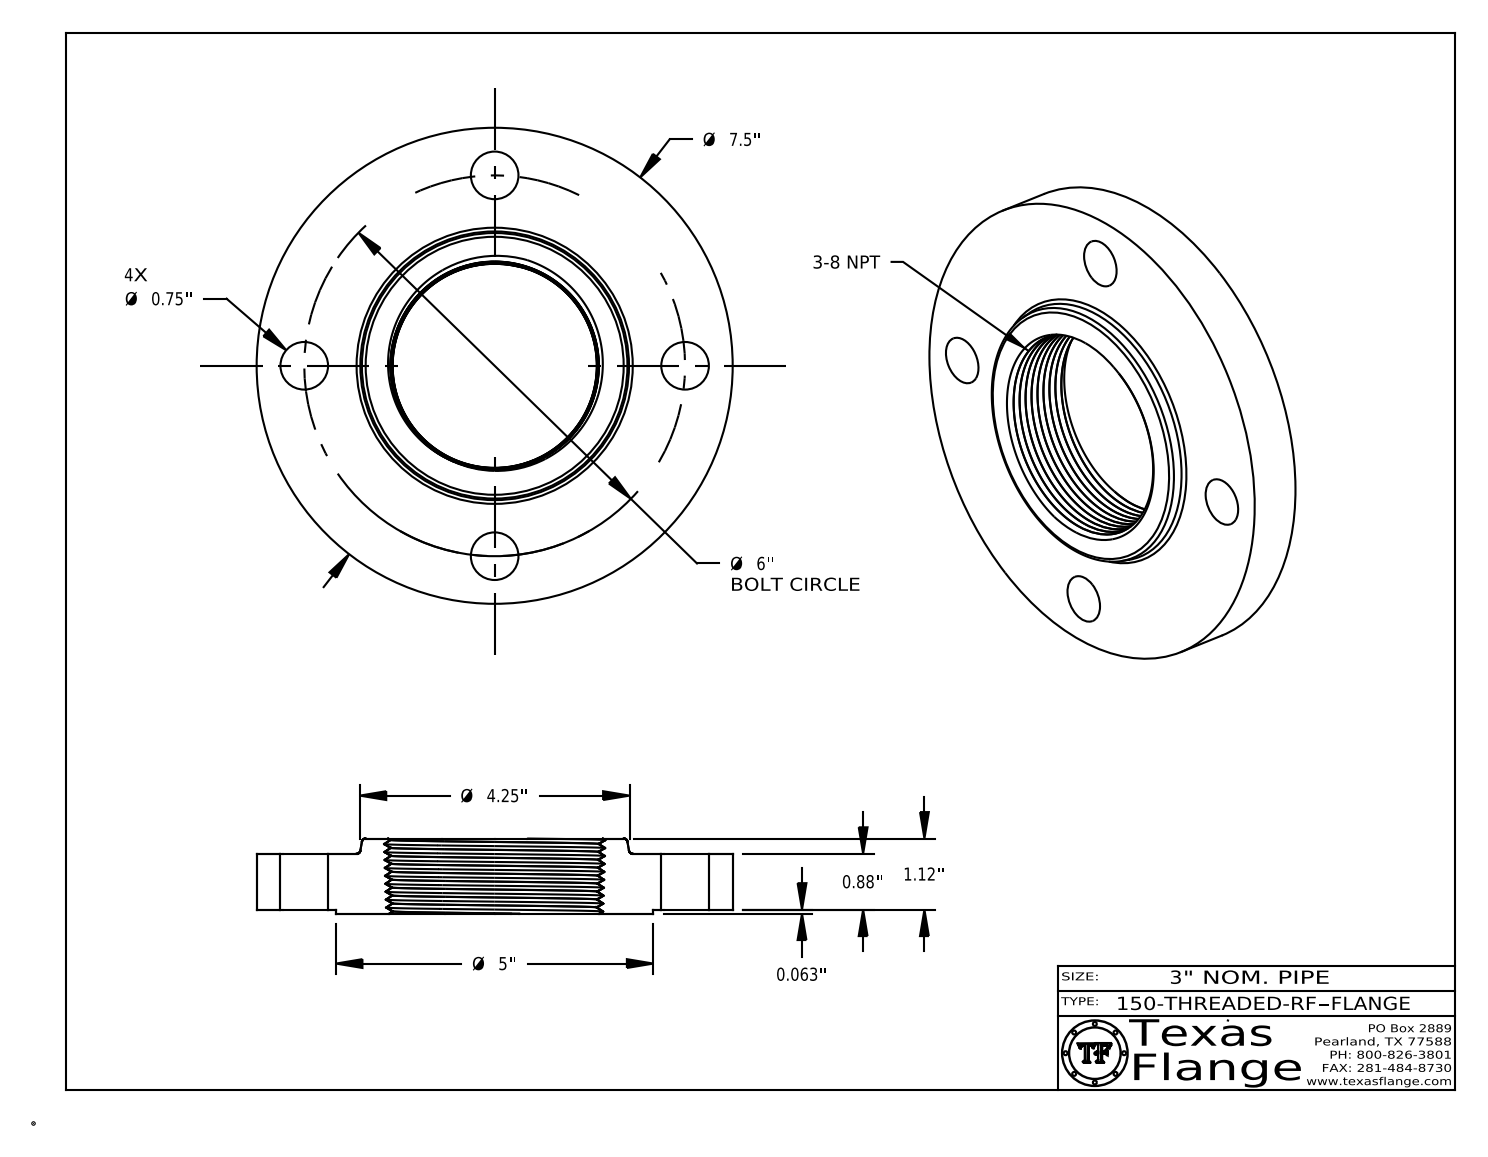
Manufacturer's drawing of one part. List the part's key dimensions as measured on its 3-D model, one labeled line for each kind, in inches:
Part name (STEP PRODUCT): 150-THREADED-RF
STEP written by: CATIA V5 STEP AP214 (AUTOMOTIVE_DESIGN)
Units: inches
Bodies: 1 solid, 509 faces (369 planar, 32 cylindrical, 108 other)
Overall size (bounding box): 7.5 × 7.5 × 1.183
Volume: 31.48 in³ · Surface area: 122.9 in²
Round holes (diameter × count): ⌀0.75 ×4, ⌀0.495 ×1
Round bosses / shafts (diameter × count): ⌀0.03 ×8, ⌀7.5 ×1, ⌀5 ×1, ⌀0.39 ×1
Main face-to-face distances: 0.88, 0.063, 0.943, 1.183, 1.12, 0.24, 0.928, 0.865, 0.015, 0.255
Hole centre spacings: 4.243, 2.296, 5.543, 6
